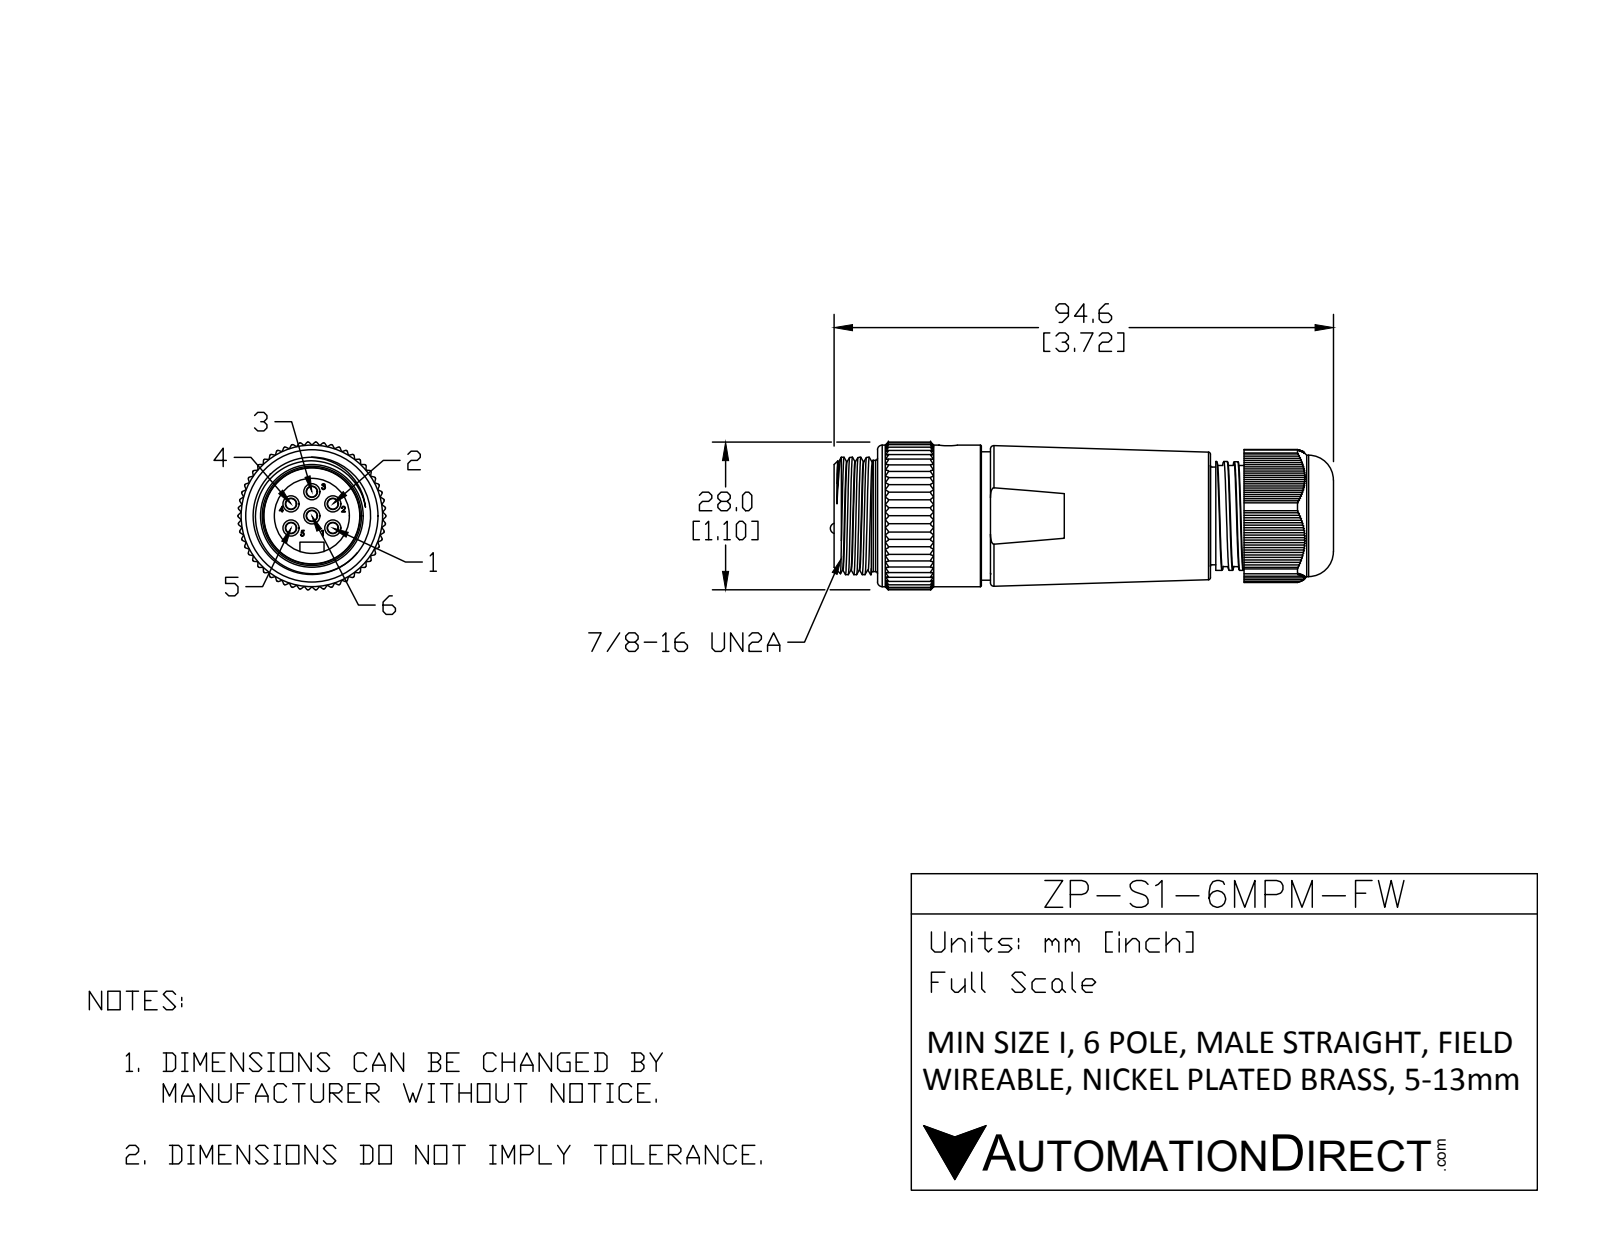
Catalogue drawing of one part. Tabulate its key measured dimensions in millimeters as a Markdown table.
| quantity | value |
| --- | --- |
| part name | ZP-S1-6MPM-FW |
| STEP written by | SolidWorks 2015 (AUTOMOTIVE_DESIGN) |
| units | millimeters |
| bodies | 10 solids, 902 faces (475 planar, 328 cylindrical, 99 other) |
| overall size | 94.64 × 27.99 × 27.98 |
| volume | 41 393 mm³ |
| surface area | 15 925 mm² |
| round holes (diameter × count) | 3.56 × 1, 13.46 × 1, 14.22 × 1, 18.28 × 1, 21.57 × 1, 24.2 × 1, 25.4 × 1 |
| round bosses / shafts (diameter × count) | 3.15 × 6, 2 × 6, 26.8 × 1, 24.3 × 1, 22.99 × 1, 22.22 × 1, 20.6 × 1, 18.14 × 1 |
| partial cylindrical surfaces (radius × count) | 0.25 × 165, 2.29 × 1, 13.23 × 1, 14 × 1 |
| main face-to-face distances | 68.78, 1.06, 0.35, 0.71, 69.78, 6.35, 8.79, 59.99, 1.41, 2.12 |
